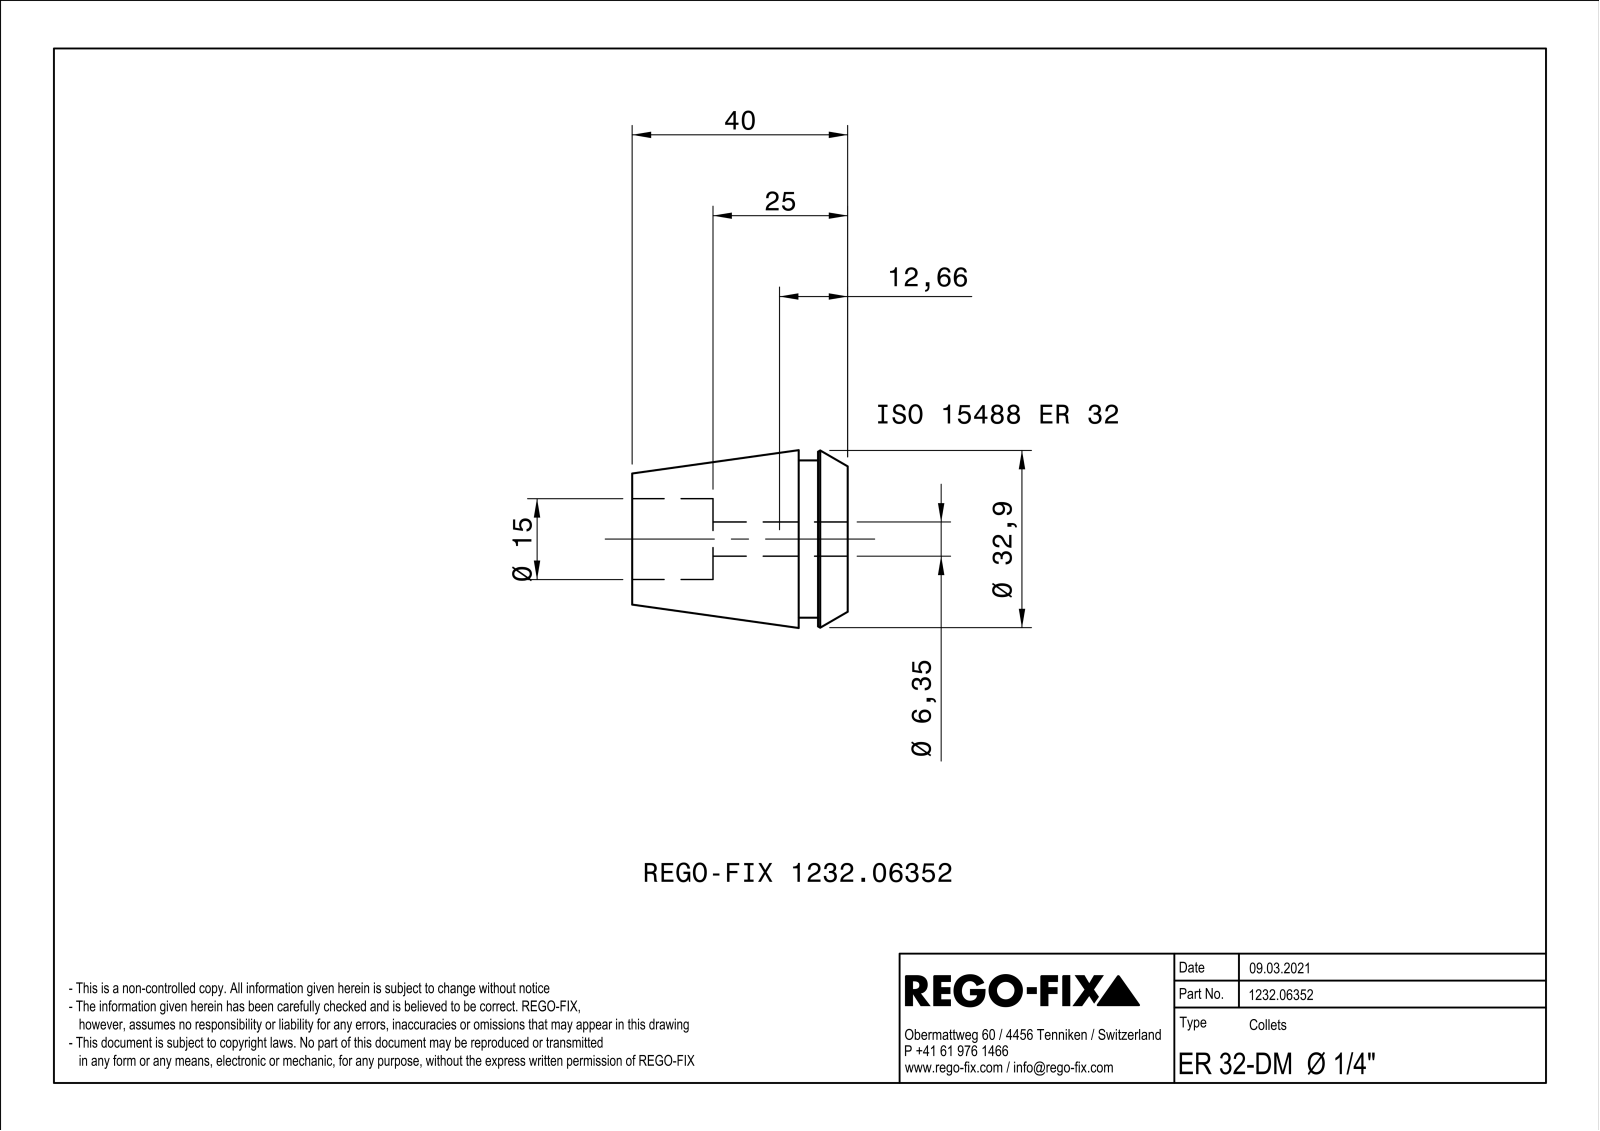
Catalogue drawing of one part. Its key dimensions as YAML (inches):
part_name: "NOCUT"
step_written_by: "SIEMENS PLM Software Solid Edge ST10 (AUTOMOTIVE_DESIGN)"
units: inches
bodies: {solids: 1, faces: 94, planar: 44, cylindrical: 9, other: 41}
overall_size: [1.575, 1.283, 1.283]
volume: 1.223
surface_area: 14.84
round_holes:
  - {diameter: 0.25, count: 1}
  - {diameter: 0.591, count: 1}
round_bosses_or_shafts:
  - {diameter: 1.15, count: 1}
face_to_face_distances: [0.031, 1.575, 0.358, 1.217, 0.217, 0.142, 1.358, 0.984, 0.768, 0.626]
